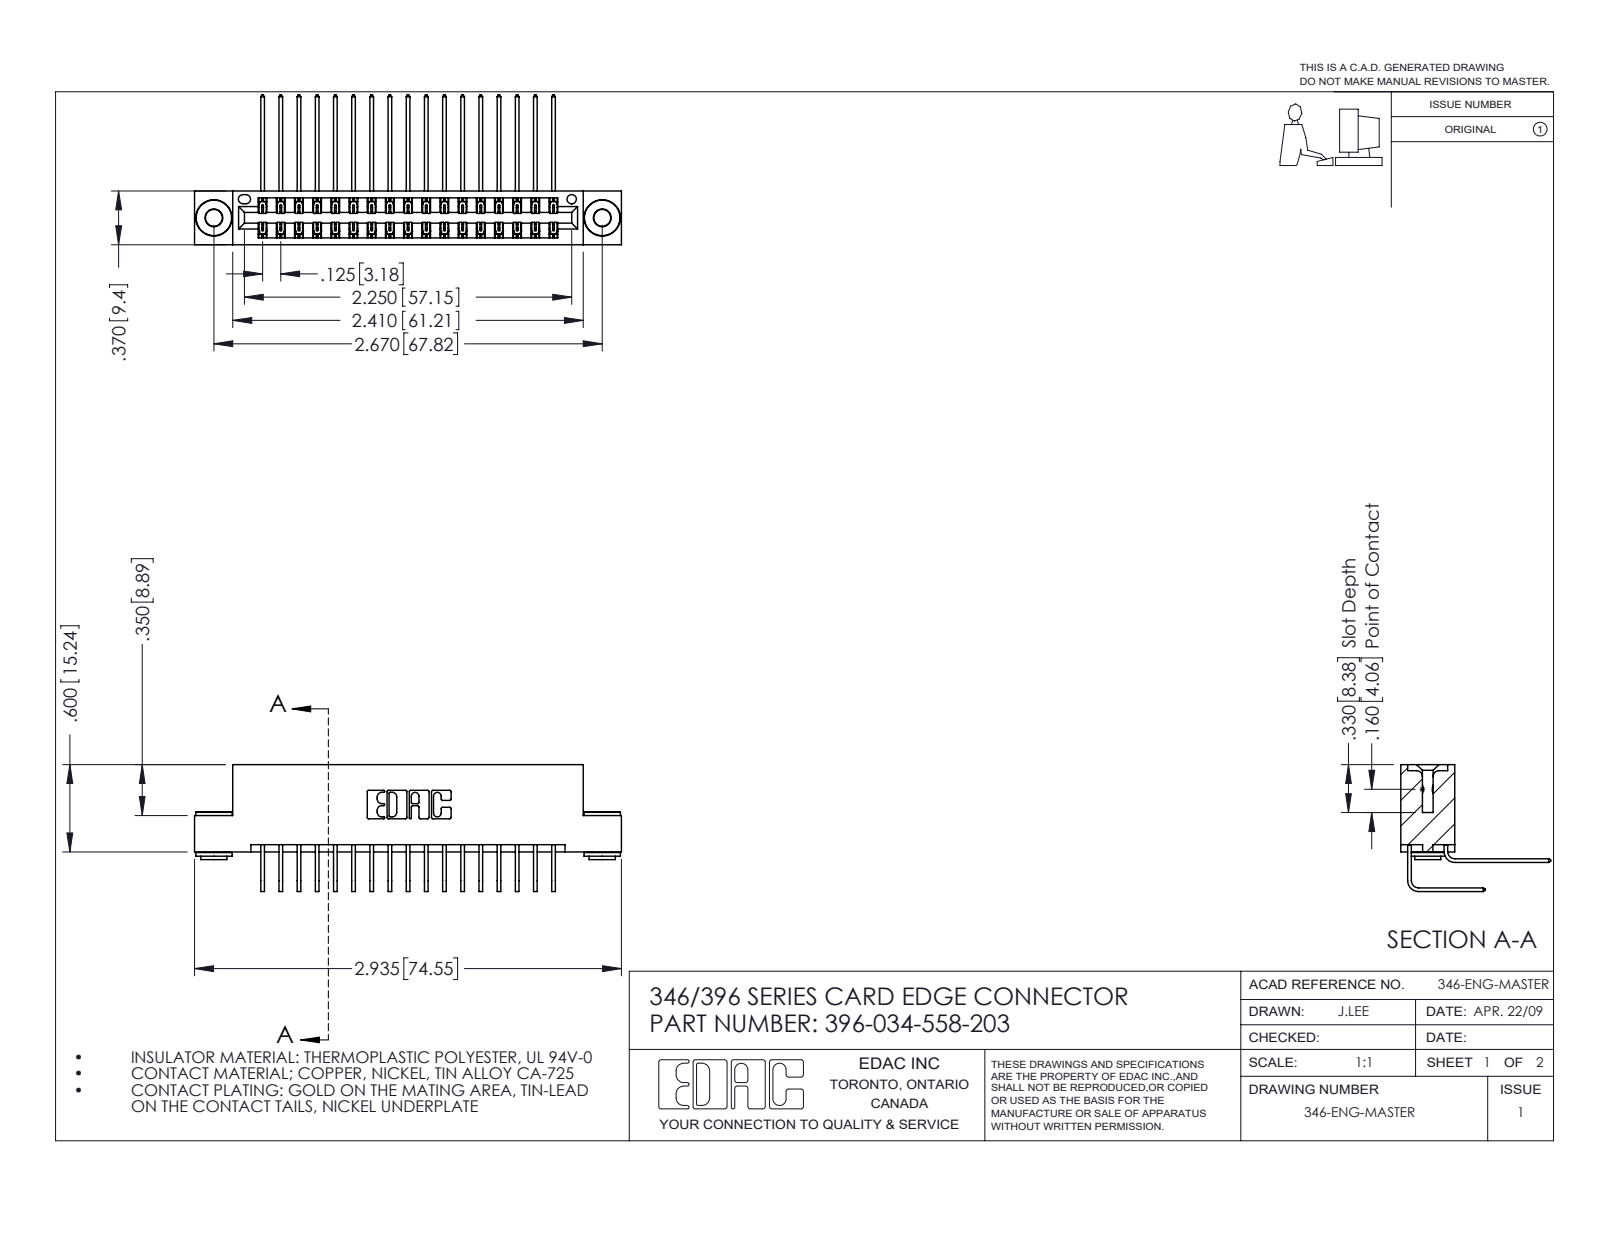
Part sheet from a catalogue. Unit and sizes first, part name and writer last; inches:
Units: inches
Overall size (bounding box): 2.935 × 1.03 × 0.873
Round holes (diameter × count): ⌀0.116 ×2, ⌀0.156 ×2, ⌀0.064 ×1
Round bosses / shafts (diameter × count): ⌀0.25 ×2, ⌀0.18 ×2, ⌀0.136 ×2
Partial cylindrical surfaces — rounded edges, fillets, slot ends (radius × count): R0.006 ×51, R0.01 ×22, R0.007 ×6, R0.031 ×6, R0.026 ×3, R0.014 ×2, R0.022 ×2, R0.024 ×2
Main face-to-face distances: 0.322, 0.048, 0.25, 0.025, 0.37, 0.298, 0.072, 0.275, 0.148, 0.222
Hole centre spacings: 0.246, 2.463, 2.67
Volume: 0.445 in³ · Surface area: 16.72 in²
Bodies: 37 solids, 1996 faces (1344 planar, 644 cylindrical, 8 other)
Part name (STEP PRODUCT): 345-250-002_345-250-002-102; 396-034-558-203; 346 Part_Flush Mounting Lugs - 0.156 Dia-TH; 345-292-001_558 559 Tail - 1 (+1 more)
STEP written by: SolidWorks 2016 (CONFIG_CONTROL_DESIGN)
